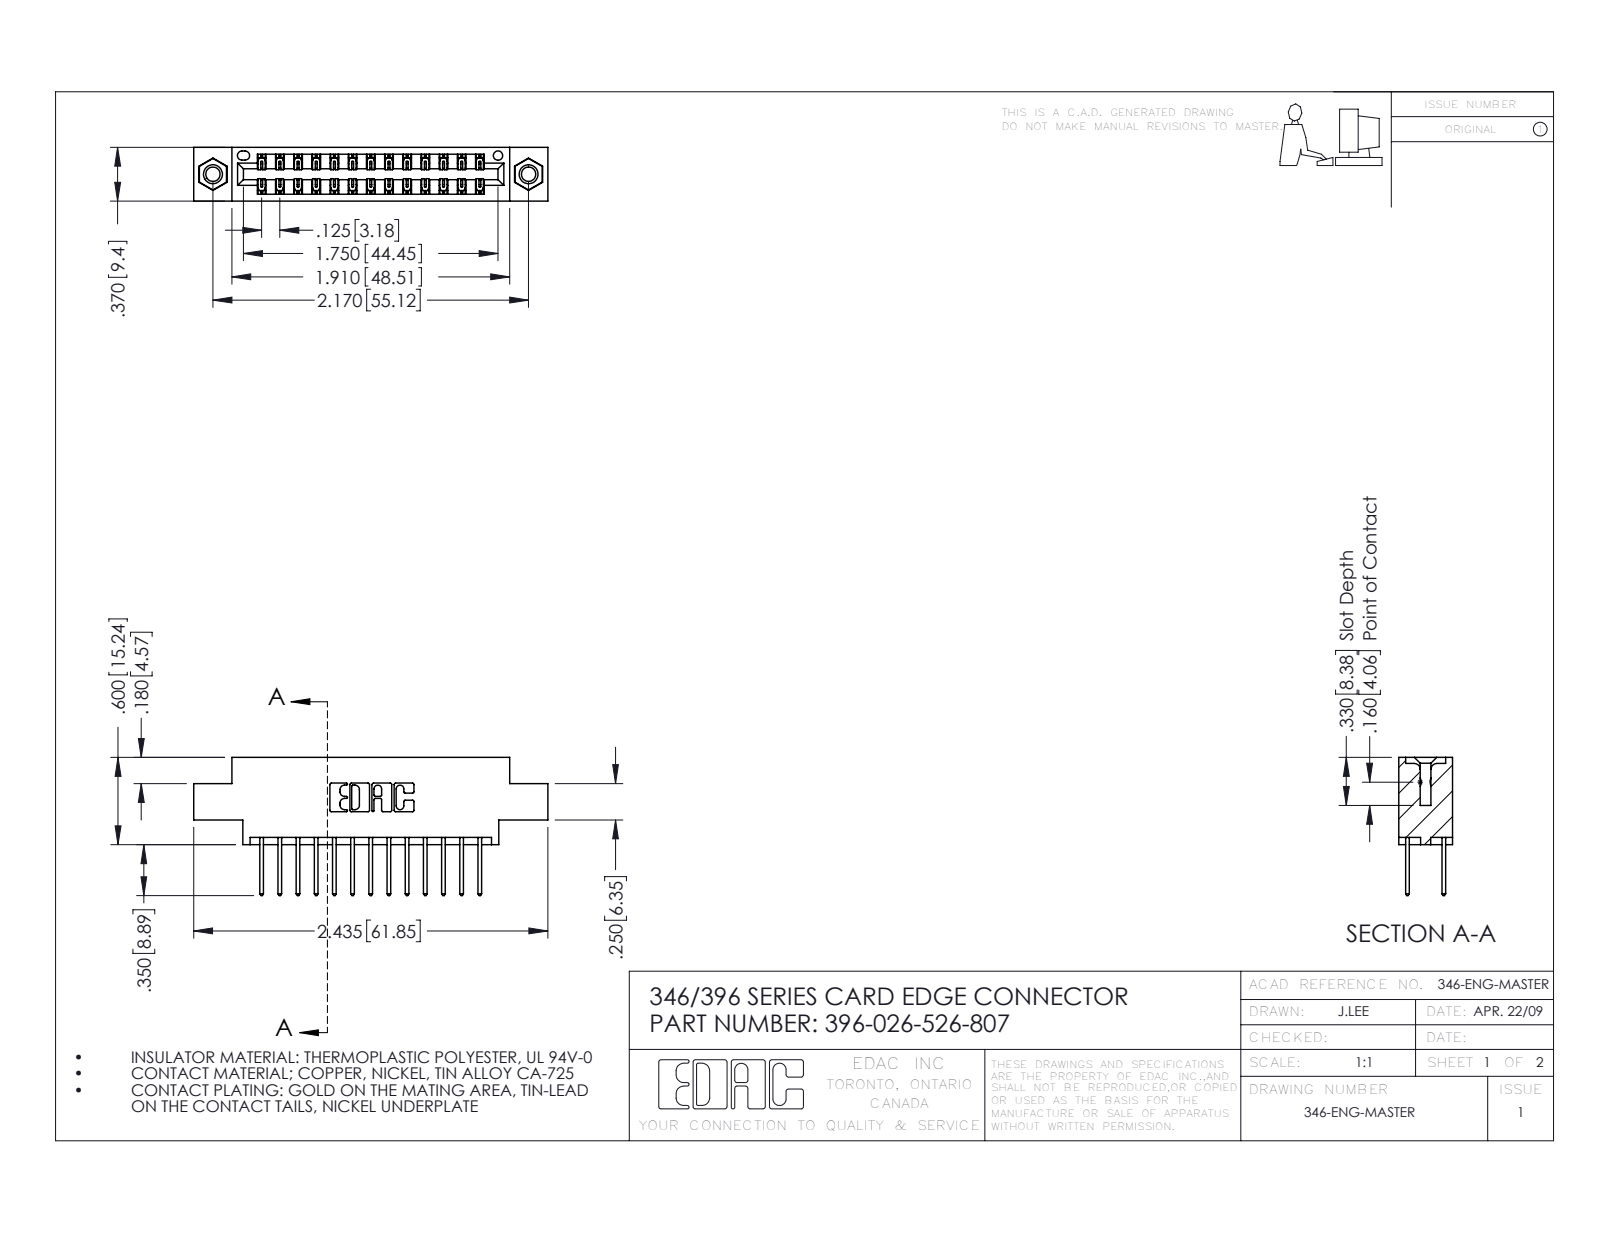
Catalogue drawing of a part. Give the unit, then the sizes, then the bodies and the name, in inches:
Units: inches
Overall size (bounding box): 2.435 × 0.95 × 0.37
Round holes (diameter × count): ⌀0.098 ×2, ⌀0.125 ×2, ⌀0.156 ×2, ⌀0.064 ×1
Round bosses / shafts (diameter × count): ⌀0.155 ×2
Partial cylindrical surfaces — rounded edges, fillets, slot ends (radius × count): R0.006 ×39, R0.01 ×26, R0.01 ×22, R0.007 ×6, R0.031 ×6, R0.026 ×3, R0.014 ×2, R0.022 ×2
Main face-to-face distances: 0.048, 0.322, 0.25, 0.37, 0.072, 0.298, 0.025, 0.275, 0.222, 0.148
Hole centre spacings: 0.246, 1.964, 2.17
Volume: 0.347 in³ · Surface area: 12.02 in²
Bodies: 29 solids, 1538 faces (1022 planar, 500 cylindrical, 16 other)
Part name (STEP PRODUCT): 345-292-001_345-293-126; 396-026-526-807; 346 Part_0.170 Offset - 0.156 Dia-TI; 345-250-001_345-250-005-103
STEP written by: SolidWorks 2016 (CONFIG_CONTROL_DESIGN)
